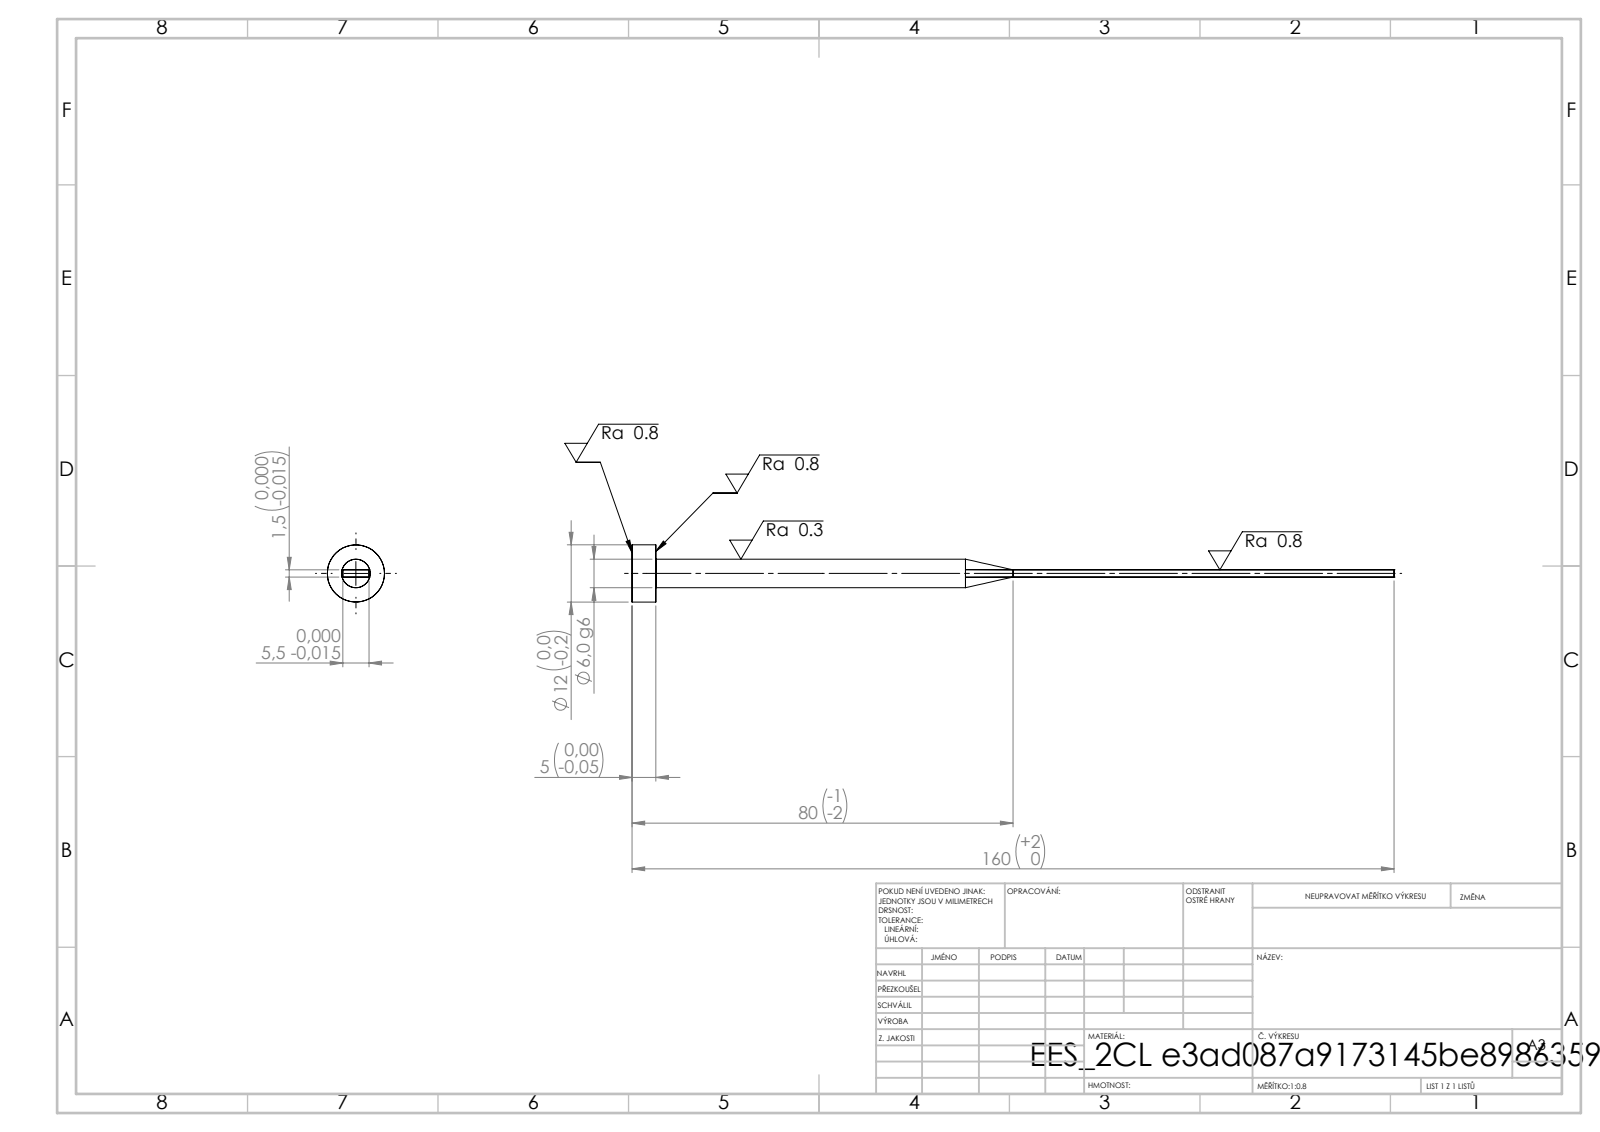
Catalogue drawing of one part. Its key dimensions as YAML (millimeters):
step_written_by: "SolidWorks 2019 (CONFIG_CONTROL_DESIGN)"
units: millimeters
bodies: {solids: 1, faces: 15, planar: 7, cylindrical: 4, other: 4}
overall_size: [160, 12, 12]
volume: 3239
surface_area: 2900
round_bosses_or_shafts:
  - {diameter: 12, count: 1}
  - {diameter: 6, count: 1}
face_to_face_distances: [1.5, 5.5, 5, 160, 155]
